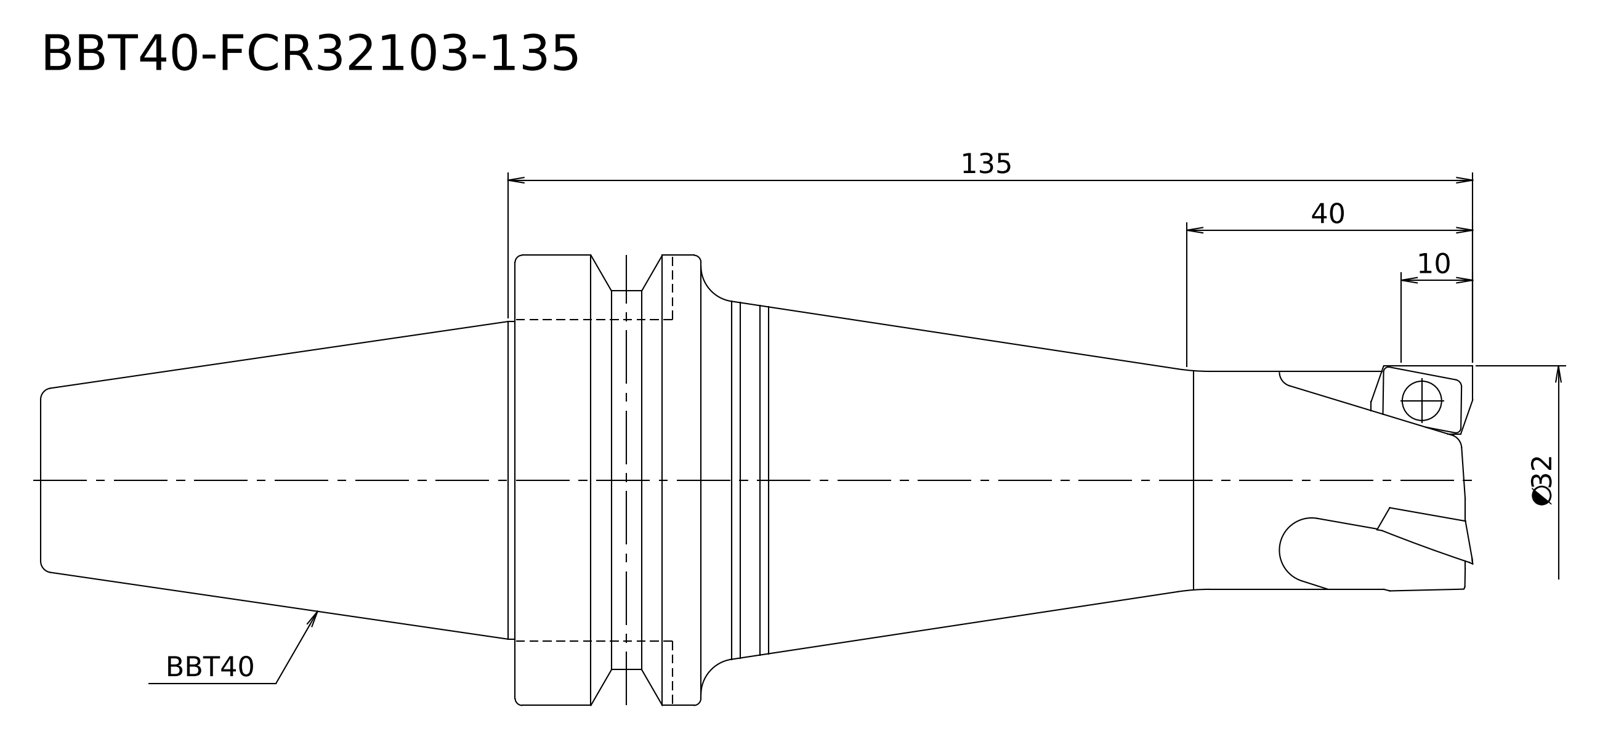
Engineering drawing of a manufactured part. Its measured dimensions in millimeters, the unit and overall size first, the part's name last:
Units: millimetres
Overall size (bounding box): 200.4 × 63 × 63
Round bosses / shafts (diameter × count): ⌀63 ×1, ⌀53 ×1, ⌀44.45 ×1, ⌀32 ×1, ⌀30.5 ×1
Main face-to-face distances: 134, 200.4, 66.4, 108, 26, 92.4
Volume: 263 949 mm³ · Surface area: 29 748 mm²
Bodies: 1 solid, 17 faces (4 planar, 6 cylindrical, 7 other)
STEP written by: Kubotek KeyCreator V8.5.1 (14335) (CONFIG_CONTROL_DESIGN)
